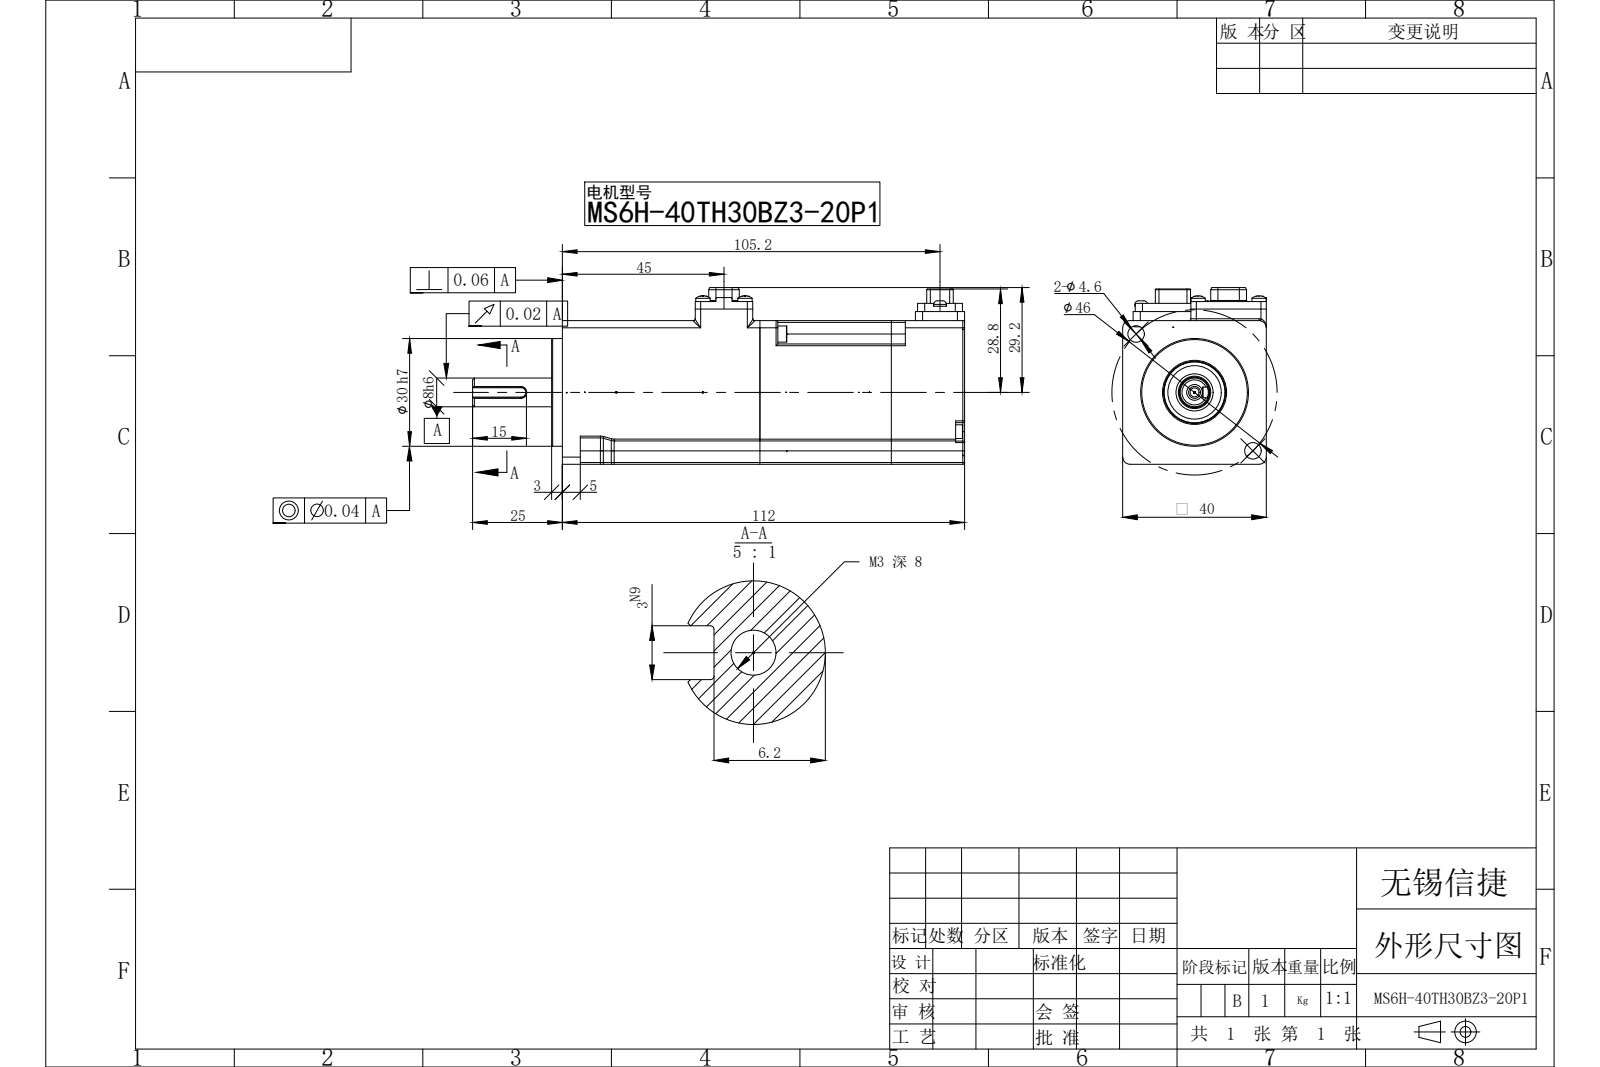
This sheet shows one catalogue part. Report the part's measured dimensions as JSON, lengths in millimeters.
{"part_name": "MS6H-40TH30BZ3-20P1", "step_written_by": "SolidWorks 2022 (CONFIG_CONTROL_DESIGN)", "units": "millimeters", "bodies": {"solids": 0, "faces": 682, "planar": 354, "cylindrical": 219, "other": 109}, "overall_size": [137, 49.2, 40], "round_holes": [[2.1, 4], [1.6, 2], [4.6, 2], [2.5, 1], [9, 1], [14.86, 1]], "round_bosses_or_shafts": [[4, 4], [3.8, 4], [4.5, 2], [3.5, 2], [30, 1], [17, 1], [10.34, 1], [8.5, 1]], "partial_cylinders_radius": [[0.5, 59], [2, 16], [0.2, 15], [0.3, 10], [3, 8], [1.5, 5], [1, 4], [2.5, 4]], "face_to_face_distances": [40, 6.5, 33.5, 112, 27, 3, 115, 2.8, 2.5, 42.5], "hole_center_spacings": [8, 16.6, 18.43, 23, 17, 45.99, 56.17, 58.2]}
